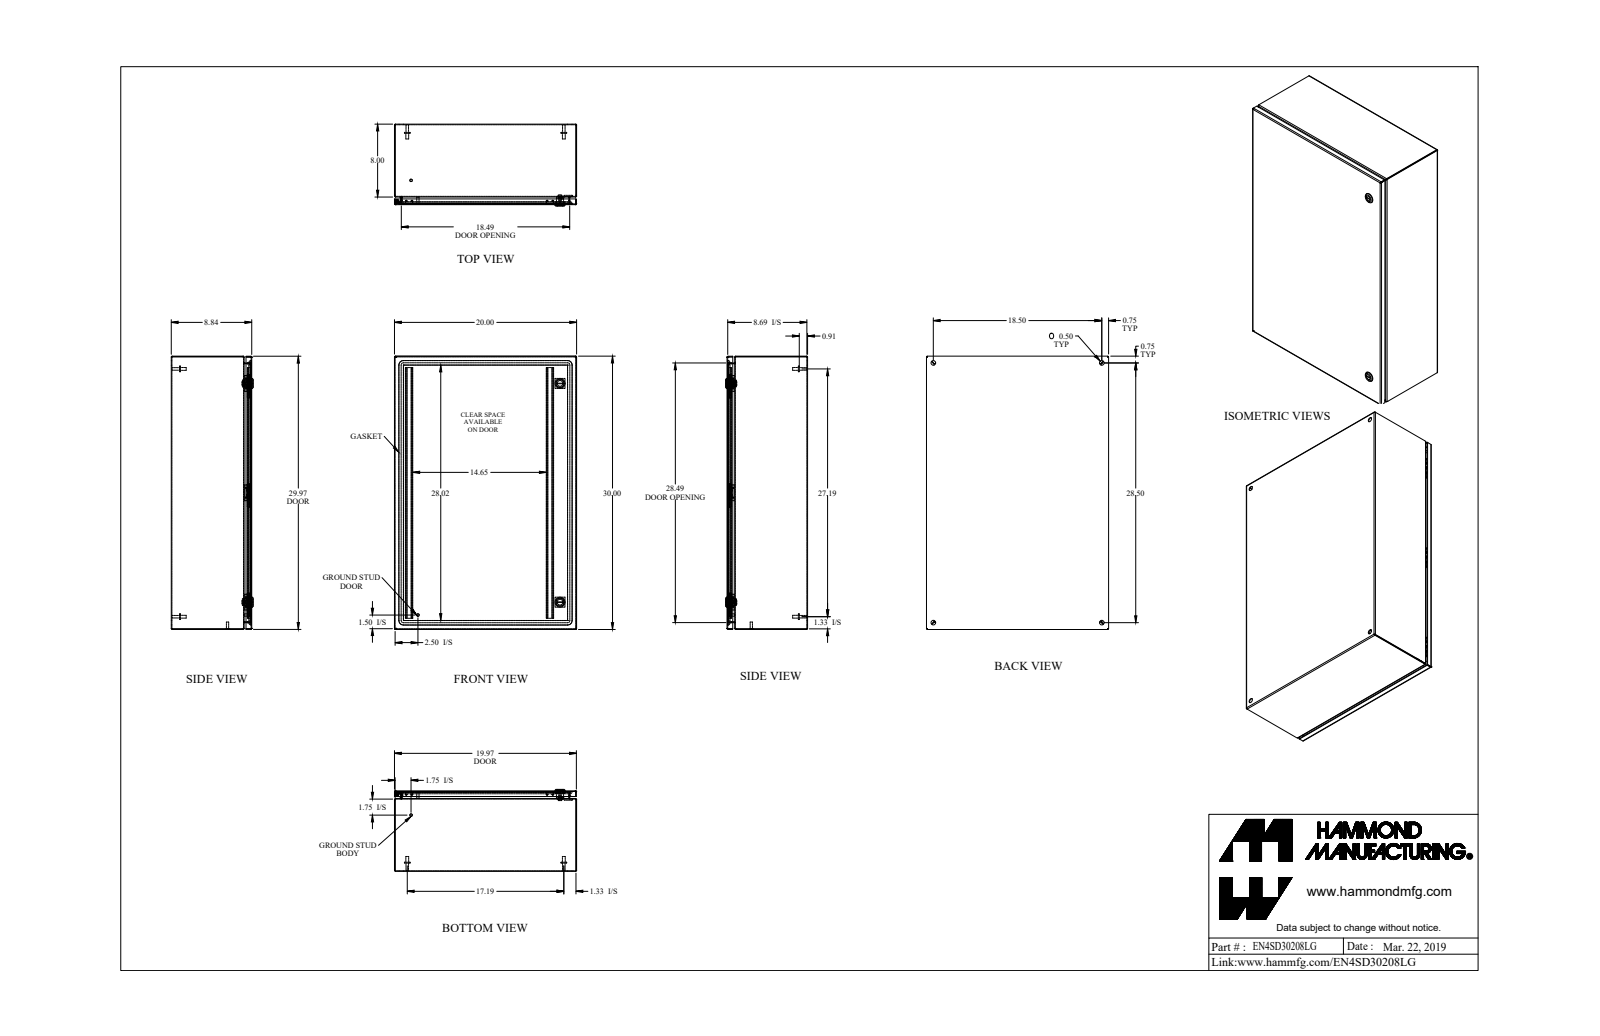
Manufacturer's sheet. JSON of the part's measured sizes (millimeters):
{"part_name": "EN4SD30208LG_Default", "step_written_by": "SolidWorks 2019 (CONFIG_CONTROL_DESIGN)", "units": "millimeters", "bodies": {"solids": 31, "faces": 885, "planar": 422, "cylindrical": 295, "other": 168}, "overall_size": [762, 508, 228.5], "volume_mm3": 2815000, "surface_area_mm2": 3115000, "round_holes": [[12.7, 4], [5.9, 2], [15.9, 2], [19.9, 2], [4.4, 1], [6.1, 1], [6.1, 1]], "round_bosses_or_shafts": [[15.9, 4], [8, 4], [6.9, 4], [27.9, 2], [13.3, 2], [7.1, 2], [6.4, 2], [11.6, 1]], "partial_cylinders_radius": [[0.9, 20], [2.7, 20], [1.1, 12], [2.1, 12], [9.7, 12], [482.7, 8], [0.2, 6], [1.6, 6]], "face_to_face_distances": [1.8, 222.6, 220.8, 224.5, 506.2, 760.2, 504.3, 508, 758.3, 762], "hole_center_spacings": [469.9, 723.9, 863, 63.3, 63.3, 446.3, 446.3, 609.6]}
